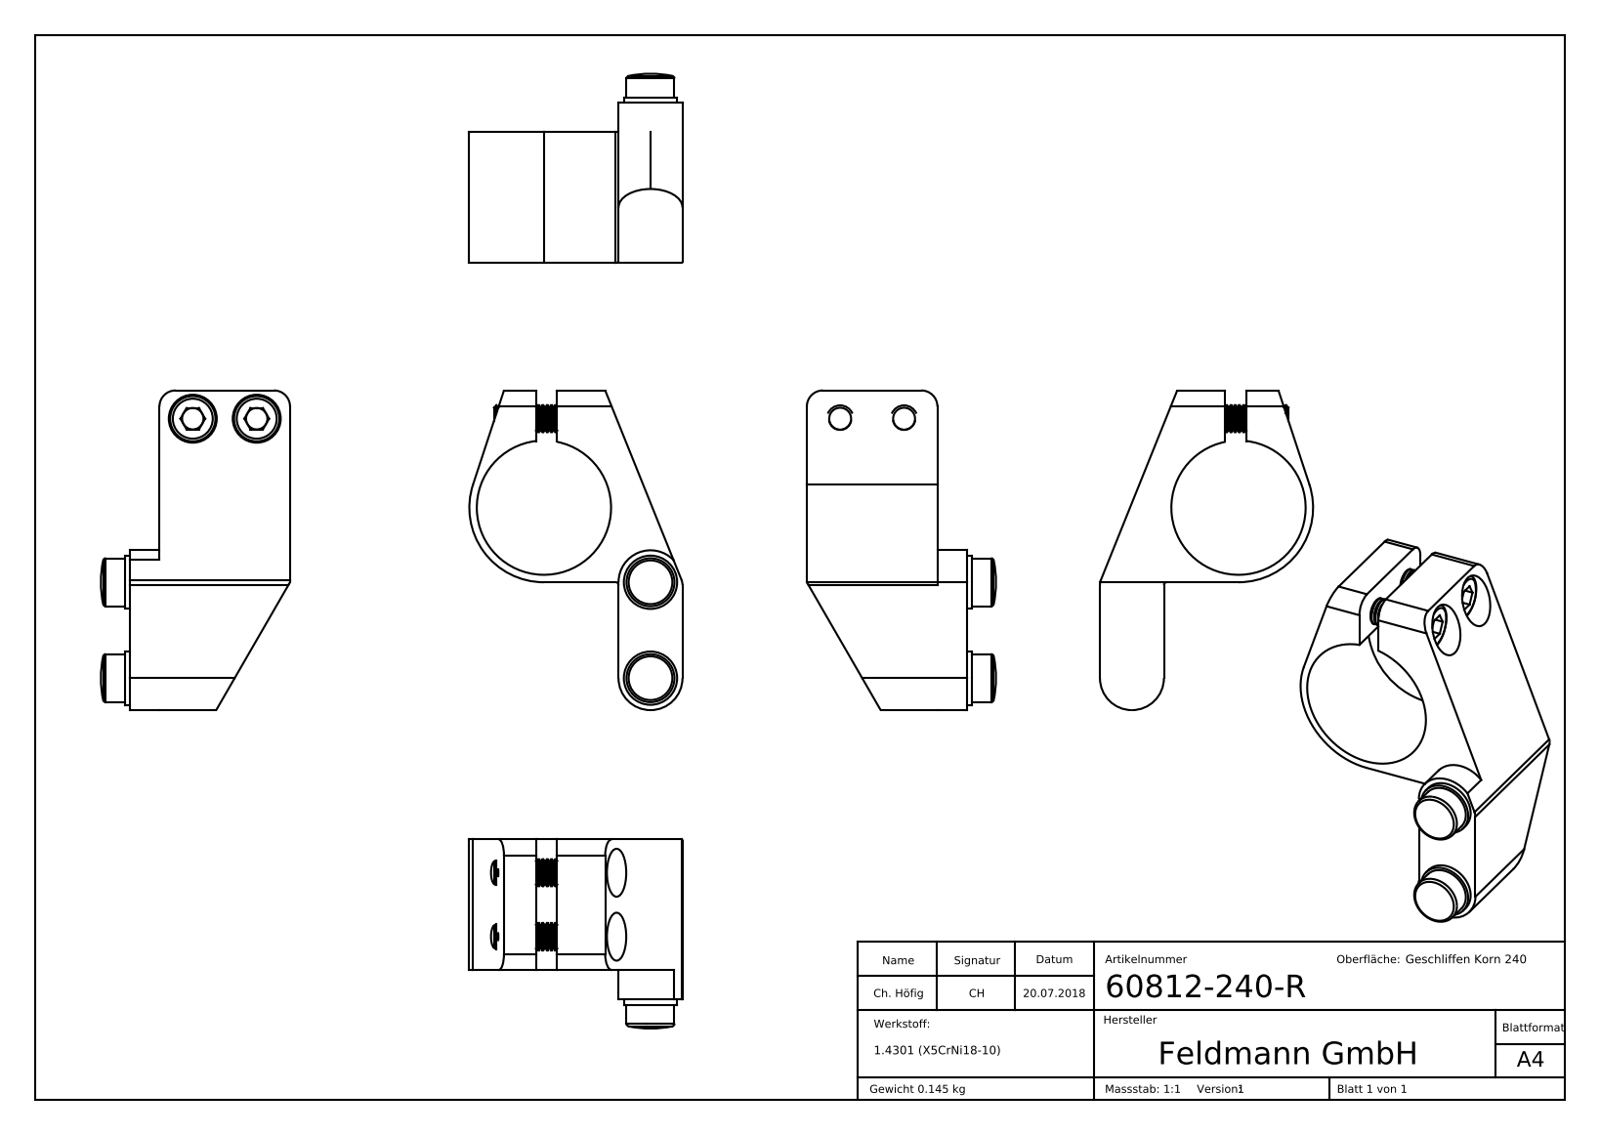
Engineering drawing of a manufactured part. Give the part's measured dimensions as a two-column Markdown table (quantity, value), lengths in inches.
| quantity | value |
| --- | --- |
| part name | 60812-240-X Teil2_60812-240-X Teil2; socket head cap screw_din_DIN 912 M5 x 16 --- 16S; 60812-240-X Teil1_60812-240-R Teil1; 60812-240-R |
| STEP written by | SolidWorks 2015 (CONFIG_CONTROL_DESIGN) |
| units | inches |
| bodies | 5 solids, 587 faces (189 planar, 117 cylindrical, 281 other) |
| overall size | 2.362 × 1.575 × 1.398 |
| volume | 1.225 in³ |
| surface area | 16.92 in² |
| round holes (diameter × count) | 0.165 × 2, 0.197 × 2, 0.205 × 2, 0.354 × 2, 0.992 × 1 |
| round bosses / shafts (diameter × count) | 0.394 × 2, 0.354 × 2, 0.335 × 2, 0.197 × 2 |
| partial cylindrical surfaces (radius × count) | 0.118 × 2, 0.236 × 2, 0.02 × 1, 0.098 × 1, 0.551 × 1 |
| main face-to-face distances | 0.965, 0.472, 1.181, 0.217, 1.417, 0.925, 0.61, 1.083, 0.453, 0.157 |
| hole center spacings | 0.472, 0.709, 0.961, 1.486 |
